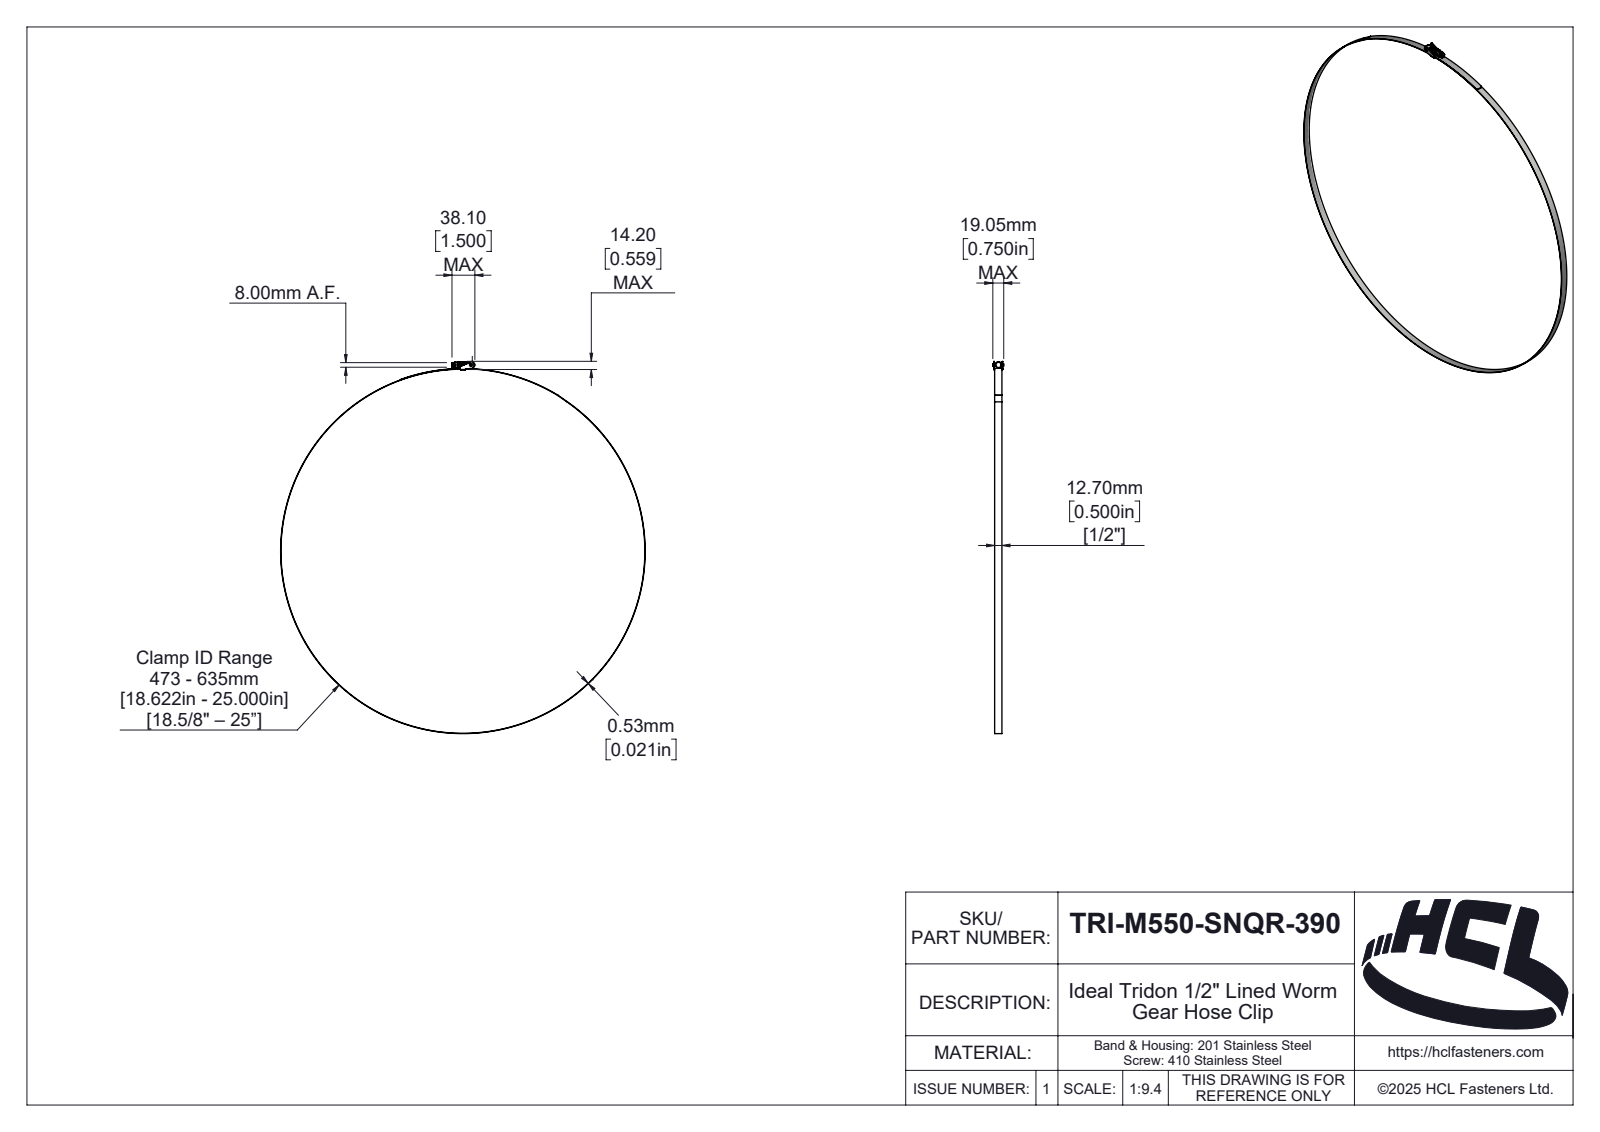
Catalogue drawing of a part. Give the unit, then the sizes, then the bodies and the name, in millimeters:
Units: millimetres
Overall size (bounding box): 649.02 × 636.06 × 19.05
Round holes (diameter × count): ⌀5 ×1, ⌀635 ×1
Round bosses / shafts (diameter × count): ⌀636.06 ×1, ⌀9.1 ×1
Partial cylindrical surfaces — rounded edges, fillets, slot ends (radius × count): R1 ×11, R0.1 ×2, R0.9 ×2, R3 ×2, R0.46 ×1, R1.89 ×1, R2 ×1, R2.35 ×1
Main face-to-face distances: 12.7, 0.8, 1.35, 14.05, 14.6, 0.55, 13.25, 0.53, 15.4, 13.8
Hole centre spacings: 325.2
Volume: 17 367 mm³ · Surface area: 59 362 mm²
Bodies: 5 solids, 222 faces (44 planar, 112 cylindrical, 66 other)
Part name (STEP PRODUCT): TRI-M550-SNQR-390
STEP written by: SolidWorks 2025 (AUTOMOTIVE_DESIGN)
